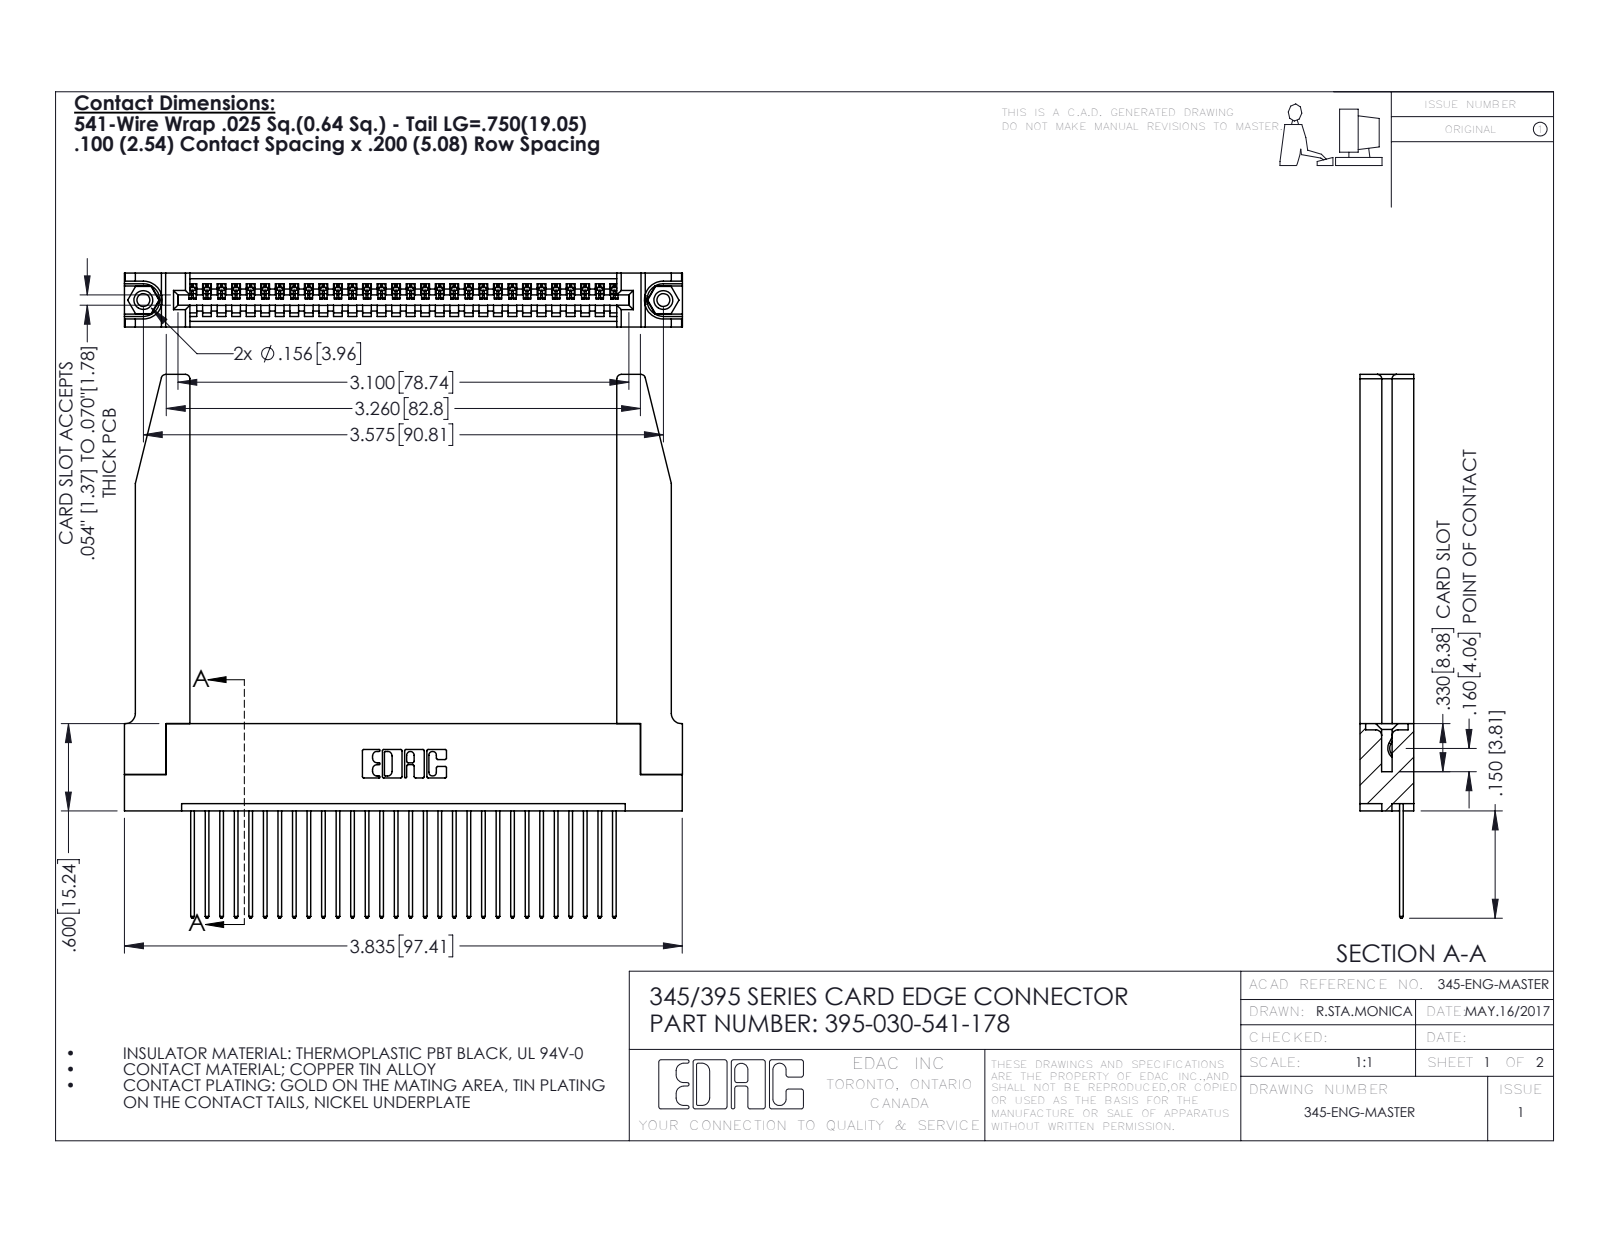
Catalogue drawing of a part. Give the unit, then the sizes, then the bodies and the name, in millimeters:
Units: millimetres
Overall size (bounding box): 97.4 × 94.9 × 9.4
Round holes (diameter × count): ⌀2.3 ×2, ⌀3.2 ×2, ⌀4 ×2, ⌀1.6 ×1
Round bosses / shafts (diameter × count): ⌀3.9 ×2
Partial cylindrical surfaces — rounded edges, fillets, slot ends (radius × count): R0.2 ×60, R0.3 ×60, R0.3 ×22, R0.8 ×8, R0.2 ×6, R0.8 ×6, R0.7 ×3, R0.8 ×2
Main face-to-face distances: 9.4, 1.8, 7.6, 5.1, 2.5, 6.9, 0.6, 3.8, 3.8, 5.7
Hole centre spacings: 6.9, 84.8, 90.8
Volume: 17 030 mm³ · Surface area: 19 560 mm²
Bodies: 35 solids, 2100 faces (1422 planar, 626 cylindrical, 52 other)
Part name (STEP PRODUCT): 395-030-541-178; 345-220-078_345-220-078; 345-250-001_345-250-001-102; 345-292-001_345-293-141 (+1 more)
STEP written by: SolidWorks 2016 (CONFIG_CONTROL_DESIGN)
